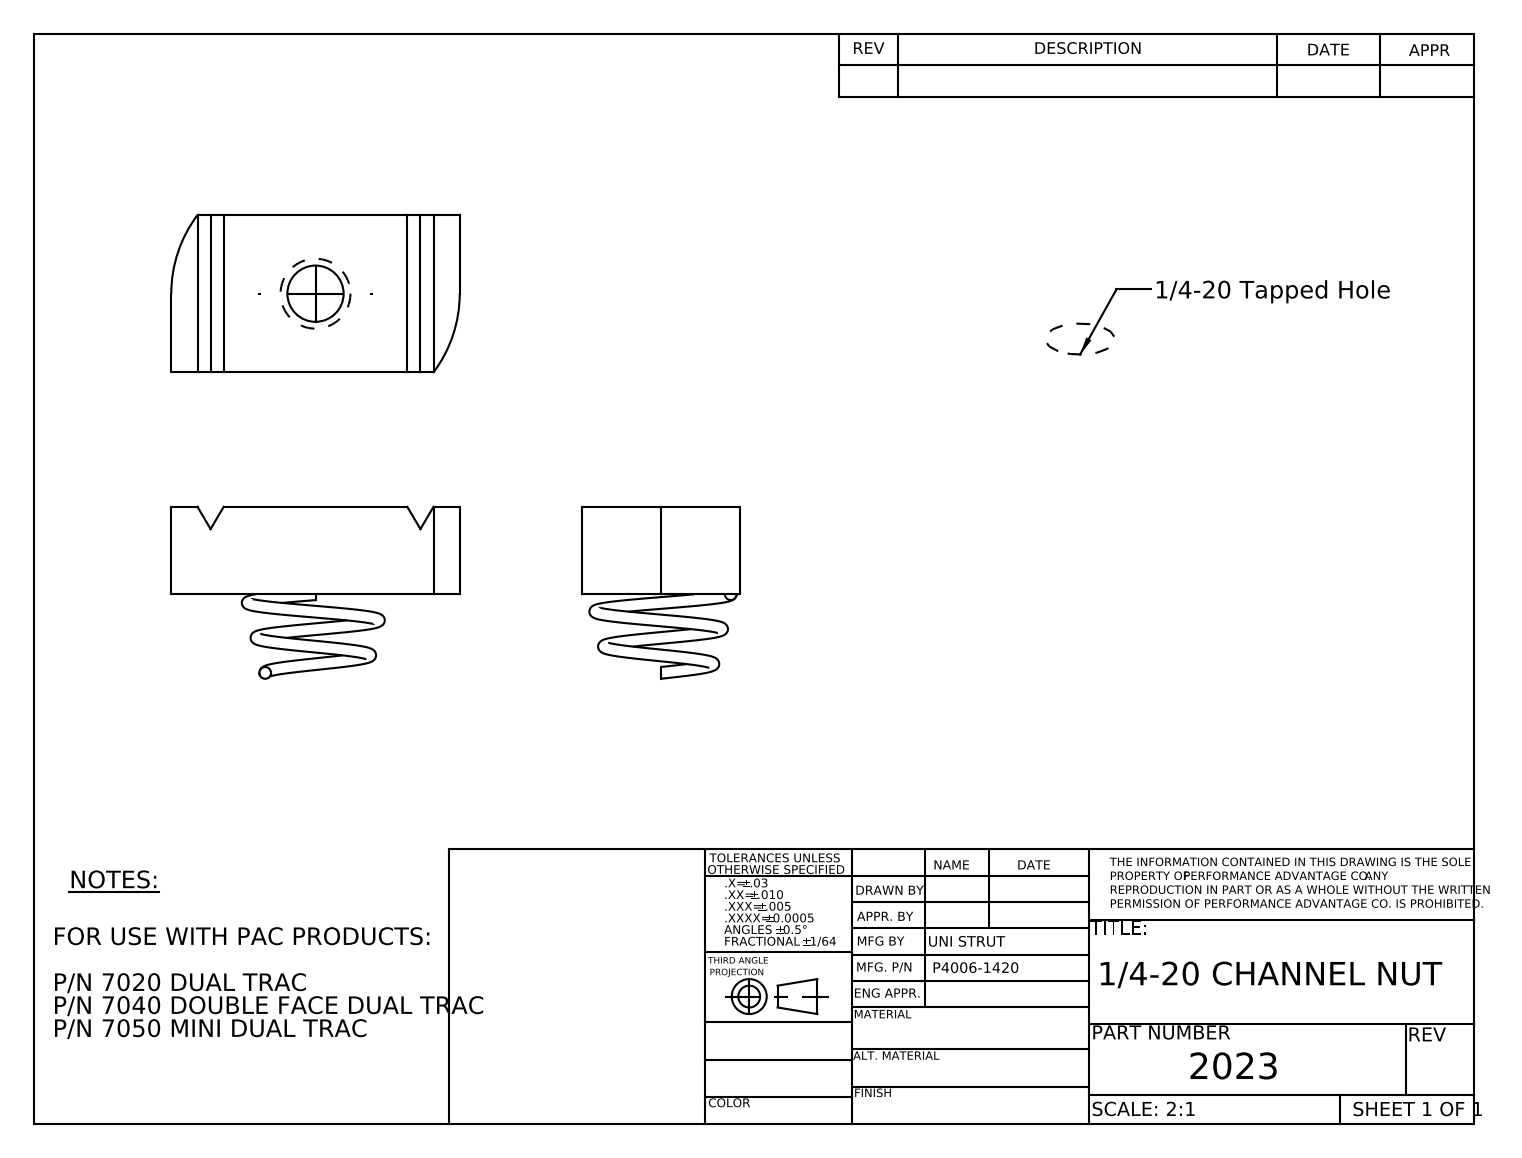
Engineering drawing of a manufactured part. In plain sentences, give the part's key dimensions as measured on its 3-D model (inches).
The part is named "2023". Its 3-D file was written by "SolidWorks 2010 (CONFIG_CONTROL_DESIGN)". It is 1 solid with 20 faces: 14 planar, 4 cylindrical and 2 other. Overall it measures 1.031 by 0.615 by 0.563 inches. Its volume is 0.166 cubic inches and its surface area 2.681 square inches. Round holes: 1 of diameter 0.201. Partial cylindrical surfaces (rounded edges, fillets, slot ends): 2 of radius 0.469. The main face-to-face distances are 0.313, 0.562, 0.646, 1.031, 0.281, 0.516.
